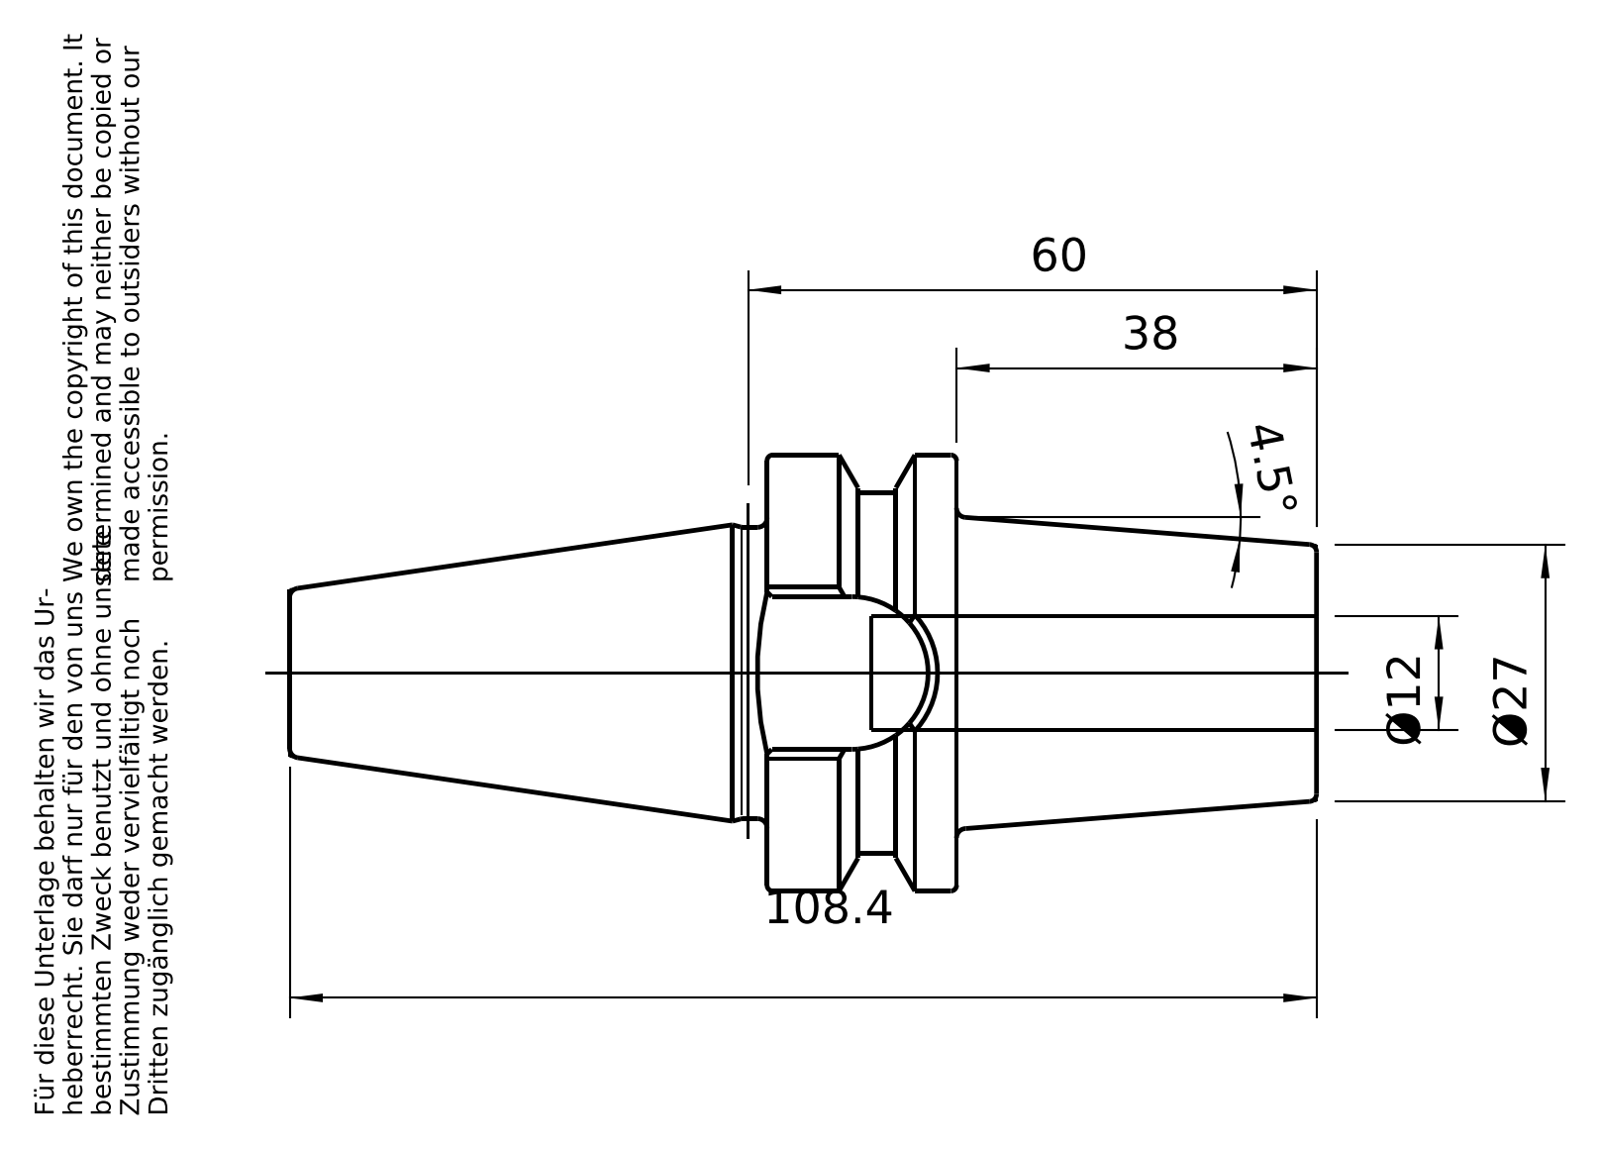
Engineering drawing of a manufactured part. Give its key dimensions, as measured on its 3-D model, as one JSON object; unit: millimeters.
{"part_name": "30-645-12", "step_written_by": "PRO/ENGINEER BY PARAMETRIC TECHNOLOGY CORPORATION, 2010430 (CONFIG_CONTROL_DESIGN)", "units": "millimeters", "bodies": {"solids": 1, "faces": 94, "planar": 26, "cylindrical": 20, "other": 48}, "overall_size": [108.4, 45.98, 45.98], "volume_mm3": 71143, "surface_area_mm2": 16858, "round_holes": [[10.11, 1], [12, 1], [12.51, 1], [13, 1]], "round_bosses_or_shafts": [[45.98, 1], [30.75, 1], [12.01, 1]], "partial_cylinders_radius": [[8.1, 1], [18.88, 1]], "face_to_face_distances": [20, 58, 38, 32.3, 11, 9, 47, 16.2, 50.4, 61.4]}
